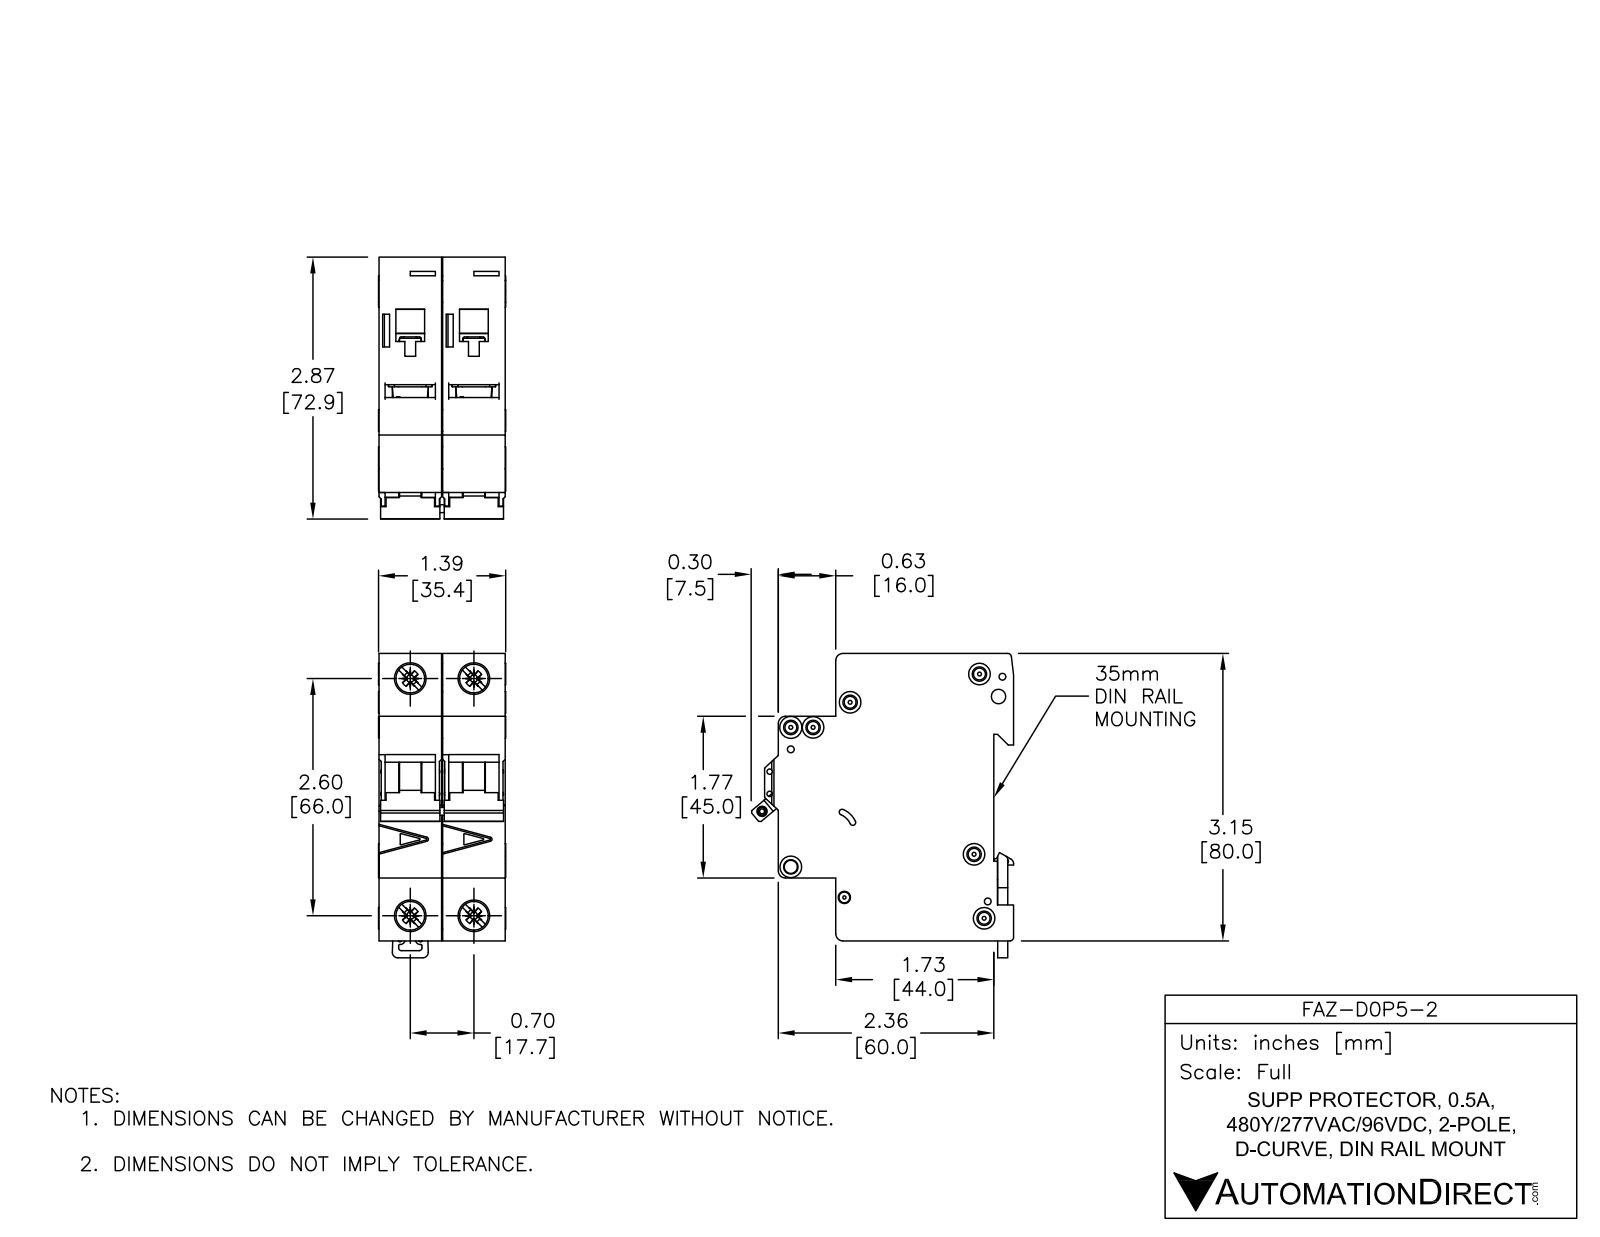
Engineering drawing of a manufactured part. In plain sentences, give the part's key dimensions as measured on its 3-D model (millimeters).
The part is named "FAZ-D0P5-2". Its 3-D file was written by "SolidWorks 2014 (AUTOMOTIVE_DESIGN)". It is 8 solids with 1104 faces: 466 planar, 396 cylindrical and 242 other. Overall it measures 84.78 by 73.04 by 35.4 millimeters. Its volume is 149 808 cubic millimeters and its surface area 38 799 square millimeters. Round holes: 6 of diameter 3.6, 3 of diameter 1.9, 2 of diameter 1.09, 2 of diameter 1.5, 2 of diameter 4, 2 of diameter 7.15, 2 of diameter 8.2, 1 of diameter 2.15, 1 of diameter 2.2, 1 of diameter 2.55, 1 of diameter 3.3, 1 of diameter 3.4. Round bosses or shafts: 4 of diameter 6, 2 of diameter 8.2, 2 of diameter 2.5. Partial cylindrical surfaces (rounded edges, fillets, slot ends): 49 of radius 0.25, 19 of radius 0.5, 10 of radius 2, 8 of radius 0.2, 8 of radius 1, 2 of radius 0.8, 2 of radius 1.8, 2 of radius 3. The main face-to-face distances are 17.7, 17.5, 35.2, 79.48, 5.5, 49.5, 44, 65.5, 60, 16. The hole center spacings are 6.2, 13.64, 17.7, 66, 68.33, 4.81, 5.19, 5.61.
